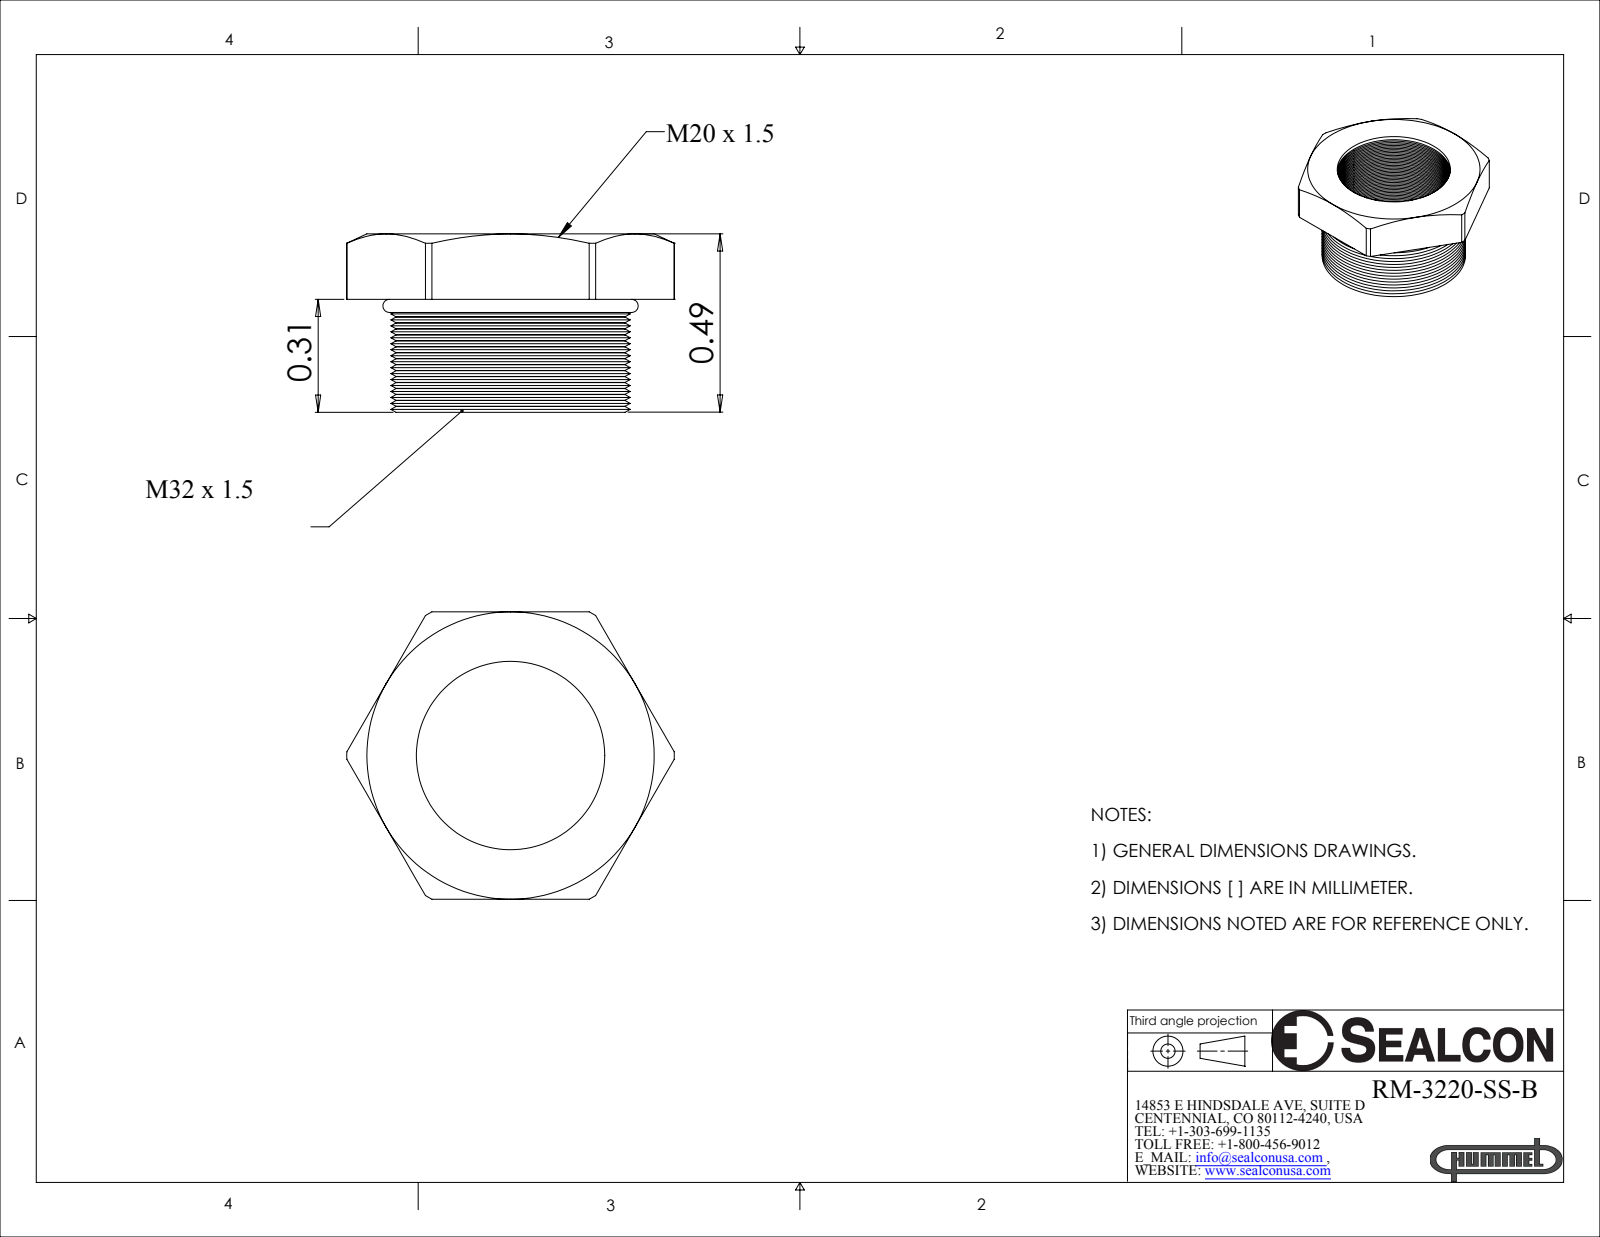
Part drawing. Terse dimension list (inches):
name: RM-3220-SS-B
written by: SolidWorks 2008 (CONFIG_CONTROL_DESIGN)
unit: in
bodies: 2 solids, 313 faces (9 planar, 105 cylindrical, 199 other)
size: 0.901 × 0.79 × 0.49
volume: 0.094 in³; area: 4.155 in²
holes: 1× ⌀0.518
bosses: 1× ⌀0.63
rounds: 1× R0.45
face distances: 0.18, 0.79, 0.31, 0.49
